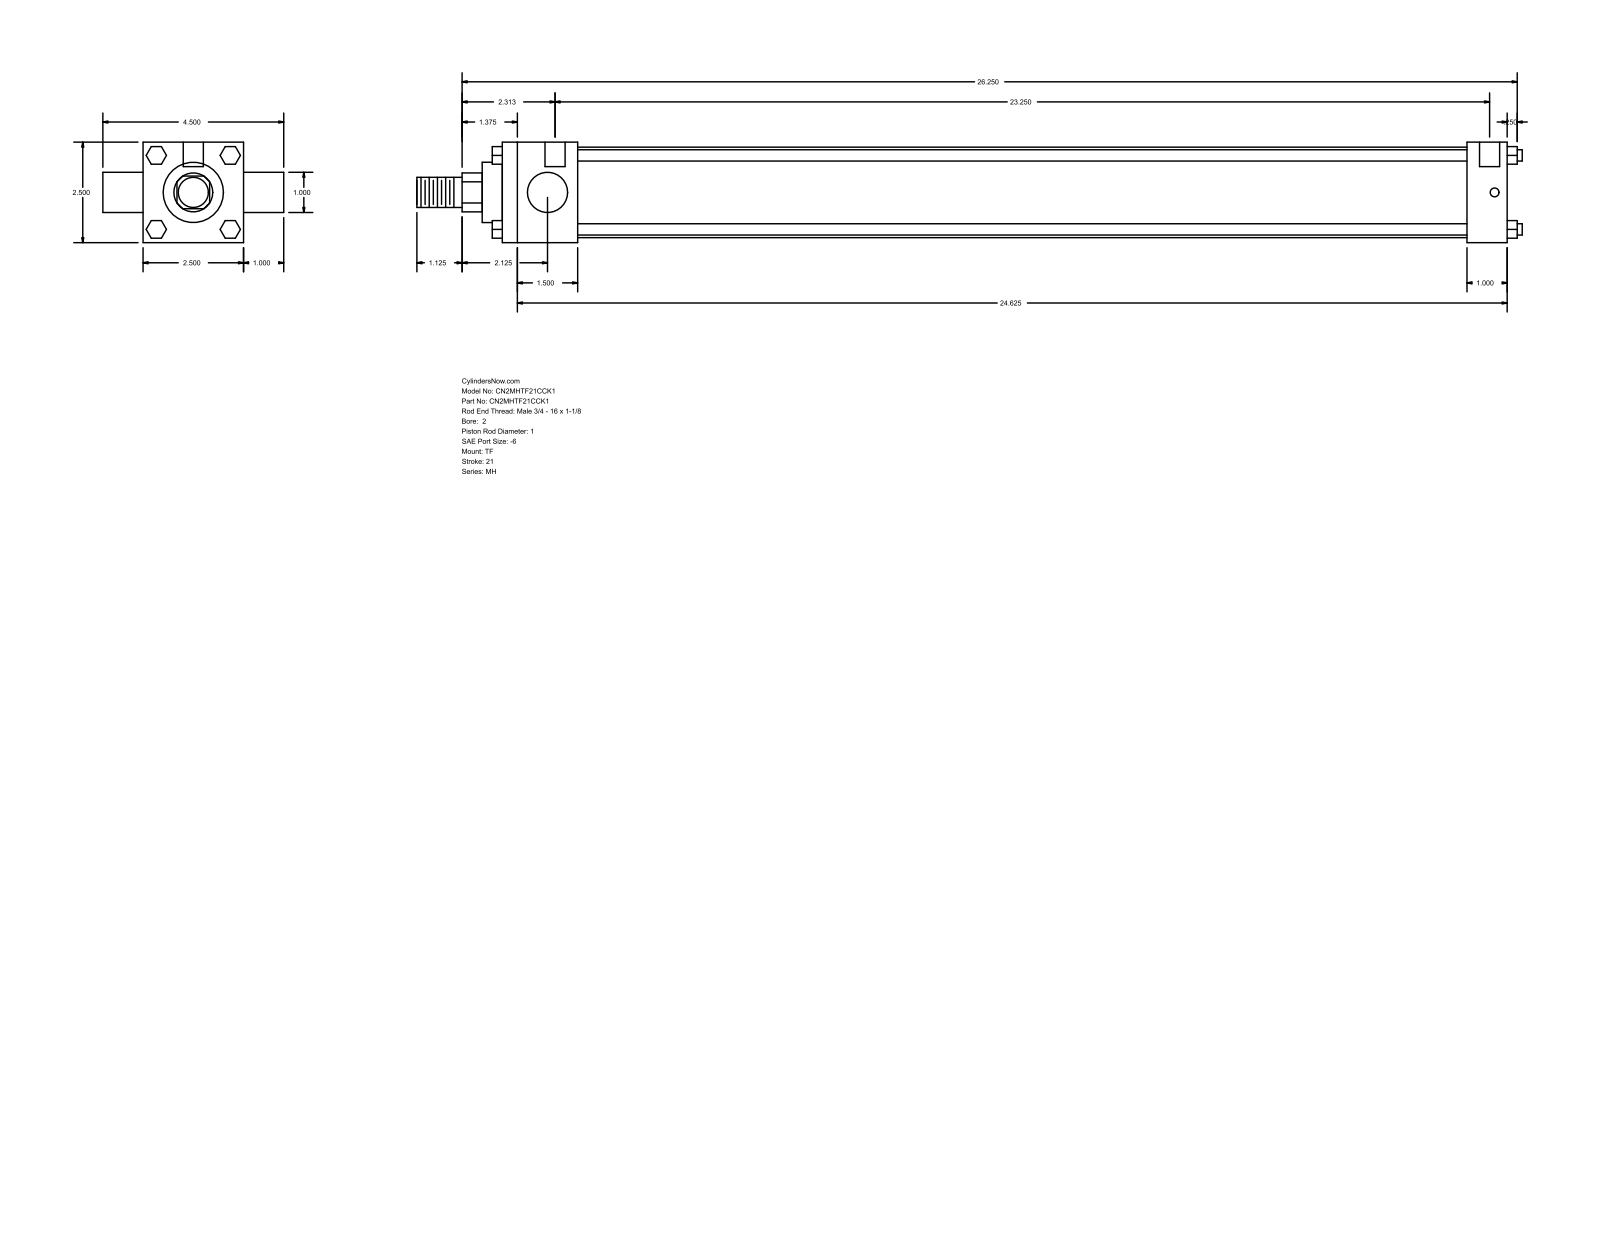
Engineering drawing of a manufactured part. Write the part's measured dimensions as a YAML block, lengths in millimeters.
part_name: "MH_TF__0200_1"
step_written_by: "GSSL Pune (CONFIG_CONTROL_DESIGN)"
units: millimeters
bodies: {solids: 0, faces: 120, planar: 92, cylindrical: 28, other: 0}
overall_size: [698.5, 114.3, 63.5]
round_holes:
  - {diameter: 5.56, count: 3}
  - {diameter: 12.7, count: 2}
round_bosses_or_shafts:
  - {diameter: 7.14, count: 4}
  - {diameter: 25.4, count: 2}
  - {diameter: 57.15, count: 1}
  - {diameter: 38.1, count: 1}
  - {diameter: 19.05, count: 1}
partial_cylinders:
  - {radius: 12.29, count: 1}
face_to_face_distances: [63.5, 635, 25.4, 47.63, 609.6, 561.97, 587.37, 88.9, 647.7, 6.35]
hole_center_spacings: [3.17, 4.76, 590.55, 593.72, 595.31, 598.48]
